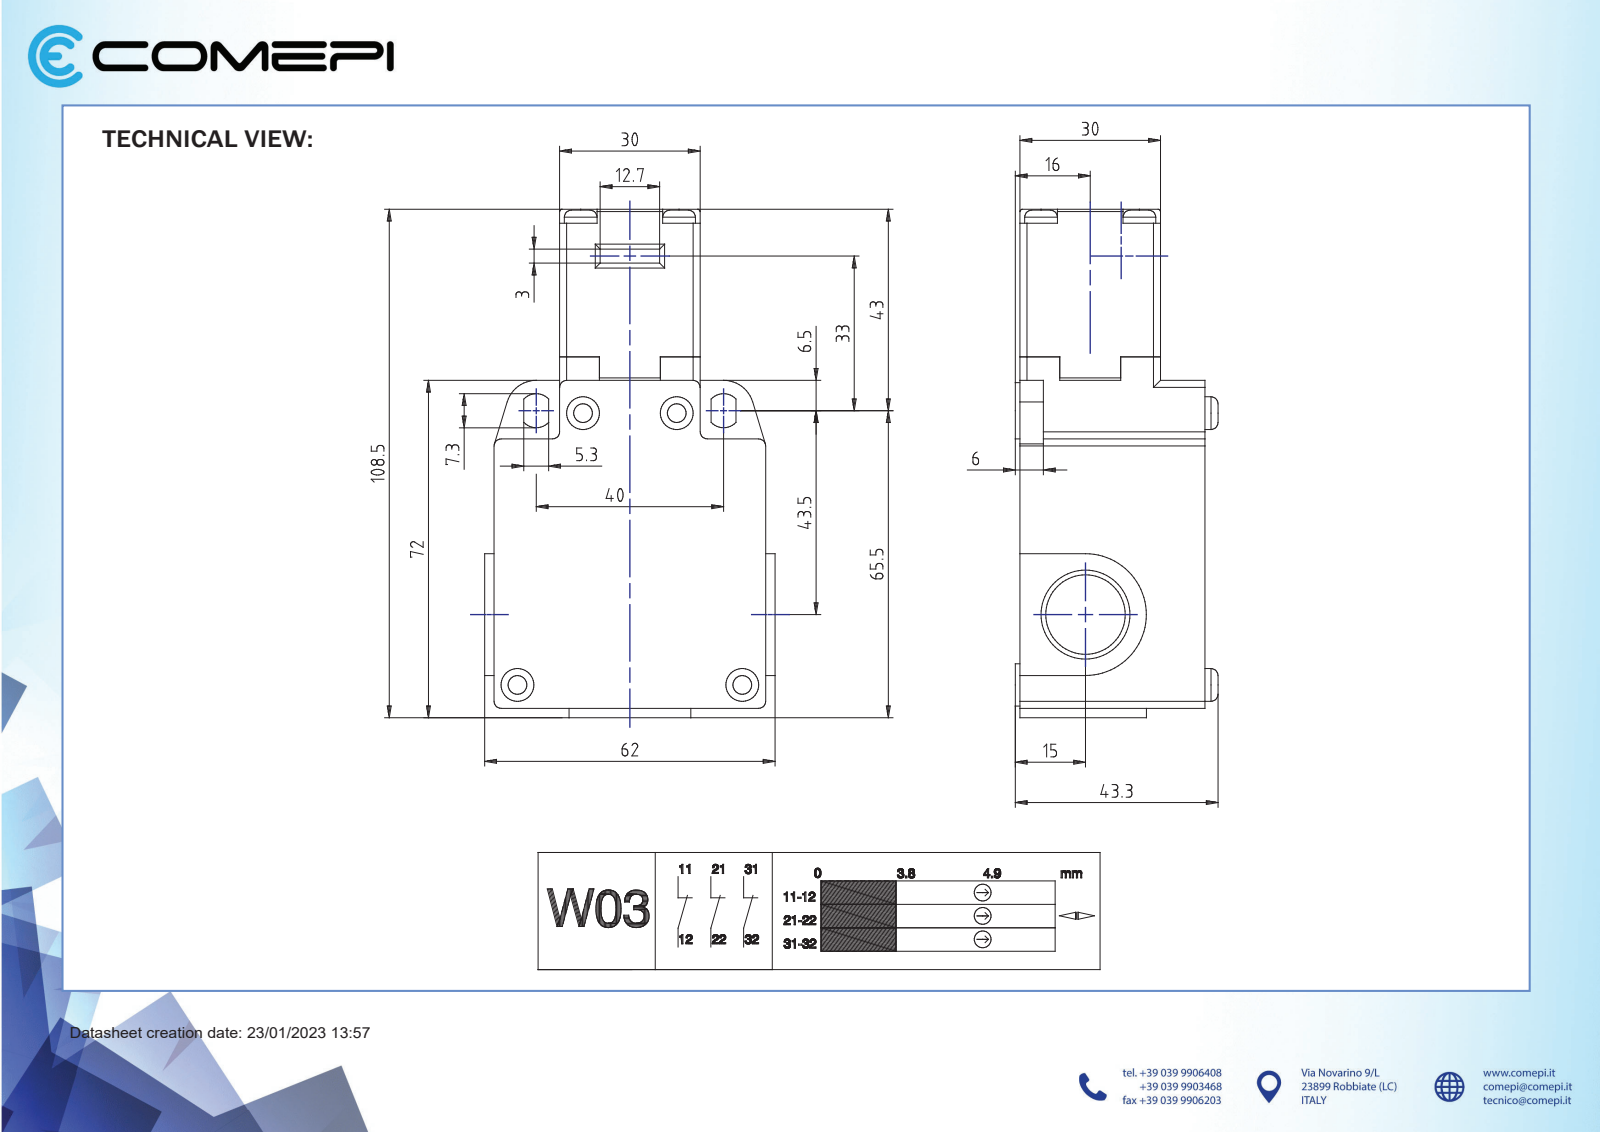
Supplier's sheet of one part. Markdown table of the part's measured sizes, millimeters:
| quantity | value |
| --- | --- |
| part name | SCM2K4000W03 |
| STEP written by | SolidWorks 2021 (CONFIG_CONTROL_DESIGN) |
| units | millimeters |
| bodies | 2 solids, 176 faces (106 planar, 59 cylindrical, 11 other) |
| overall size | 108.5 × 62 × 43.3 |
| volume | 177 600 mm³ |
| surface area | 28 080 mm² |
| round holes (diameter × count) | 7 × 4, 17 × 2, 19 × 2 |
| round bosses / shafts (diameter × count) | 7 × 4, 12 × 2, 9 × 2 |
| partial cylindrical surfaces (radius × count) | 1.5 × 12, 0.5 × 4, 3.7 × 2, 6.5 × 2, 13 × 2, 11.5 × 1, 12 × 1 |
| main face-to-face distances | 39.5, 44, 14, 30, 58, 2, 6, 9.5, 70, 3 |
| hole center spacings | 21, 14.1, 15.6, 29.7 |
